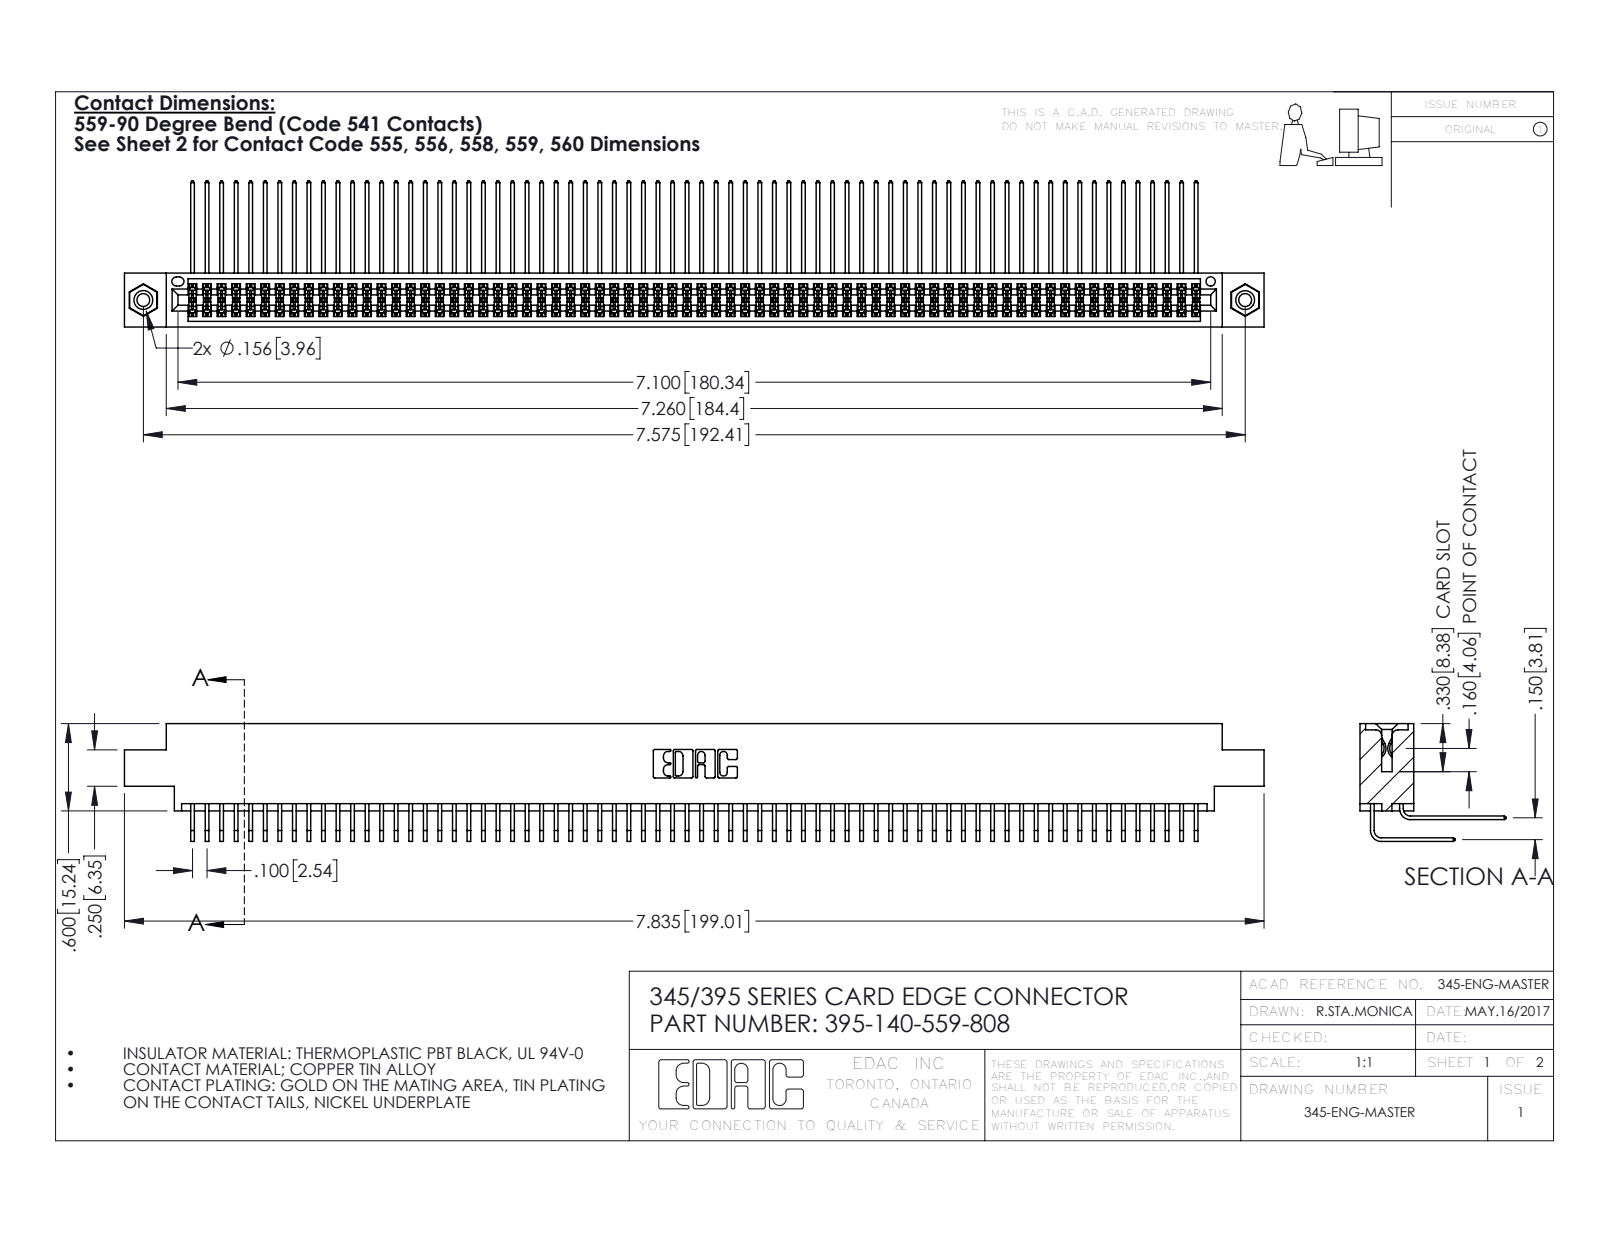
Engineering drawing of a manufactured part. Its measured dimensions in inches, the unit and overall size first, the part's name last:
Units: inches
Overall size (bounding box): 7.835 × 1.005 × 0.809
Round holes (diameter × count): ⌀0.089 ×2, ⌀0.125 ×2, ⌀0.156 ×2, ⌀0.064 ×1
Round bosses / shafts (diameter × count): ⌀0.155 ×2
Partial cylindrical surfaces — rounded edges, fillets, slot ends (radius × count): R0.006 ×279, R0.01 ×22, R0.007 ×6, R0.031 ×6, R0.026 ×3, R0.014 ×2, R0.019 ×2, R0.022 ×2
Main face-to-face distances: 0.072, 0.298, 0.2, 0.37, 0.098, 0.272, 0.025, 0.225, 0.175, 0.15
Hole centre spacings: 0.27, 7.339, 7.575
Volume: 1.238 in³ · Surface area: 53.43 in²
Bodies: 143 solids, 7470 faces (5016 planar, 2438 cylindrical, 16 other)
Part name (STEP PRODUCT): 395-140-559-808; 345 Part_0.170 Offset - 0.156 Dia-TI; 345-292-001_559 Tail - 2; 345-292-001_558 559 Tail - 1 (+1 more)
STEP written by: SolidWorks 2016 (CONFIG_CONTROL_DESIGN)
